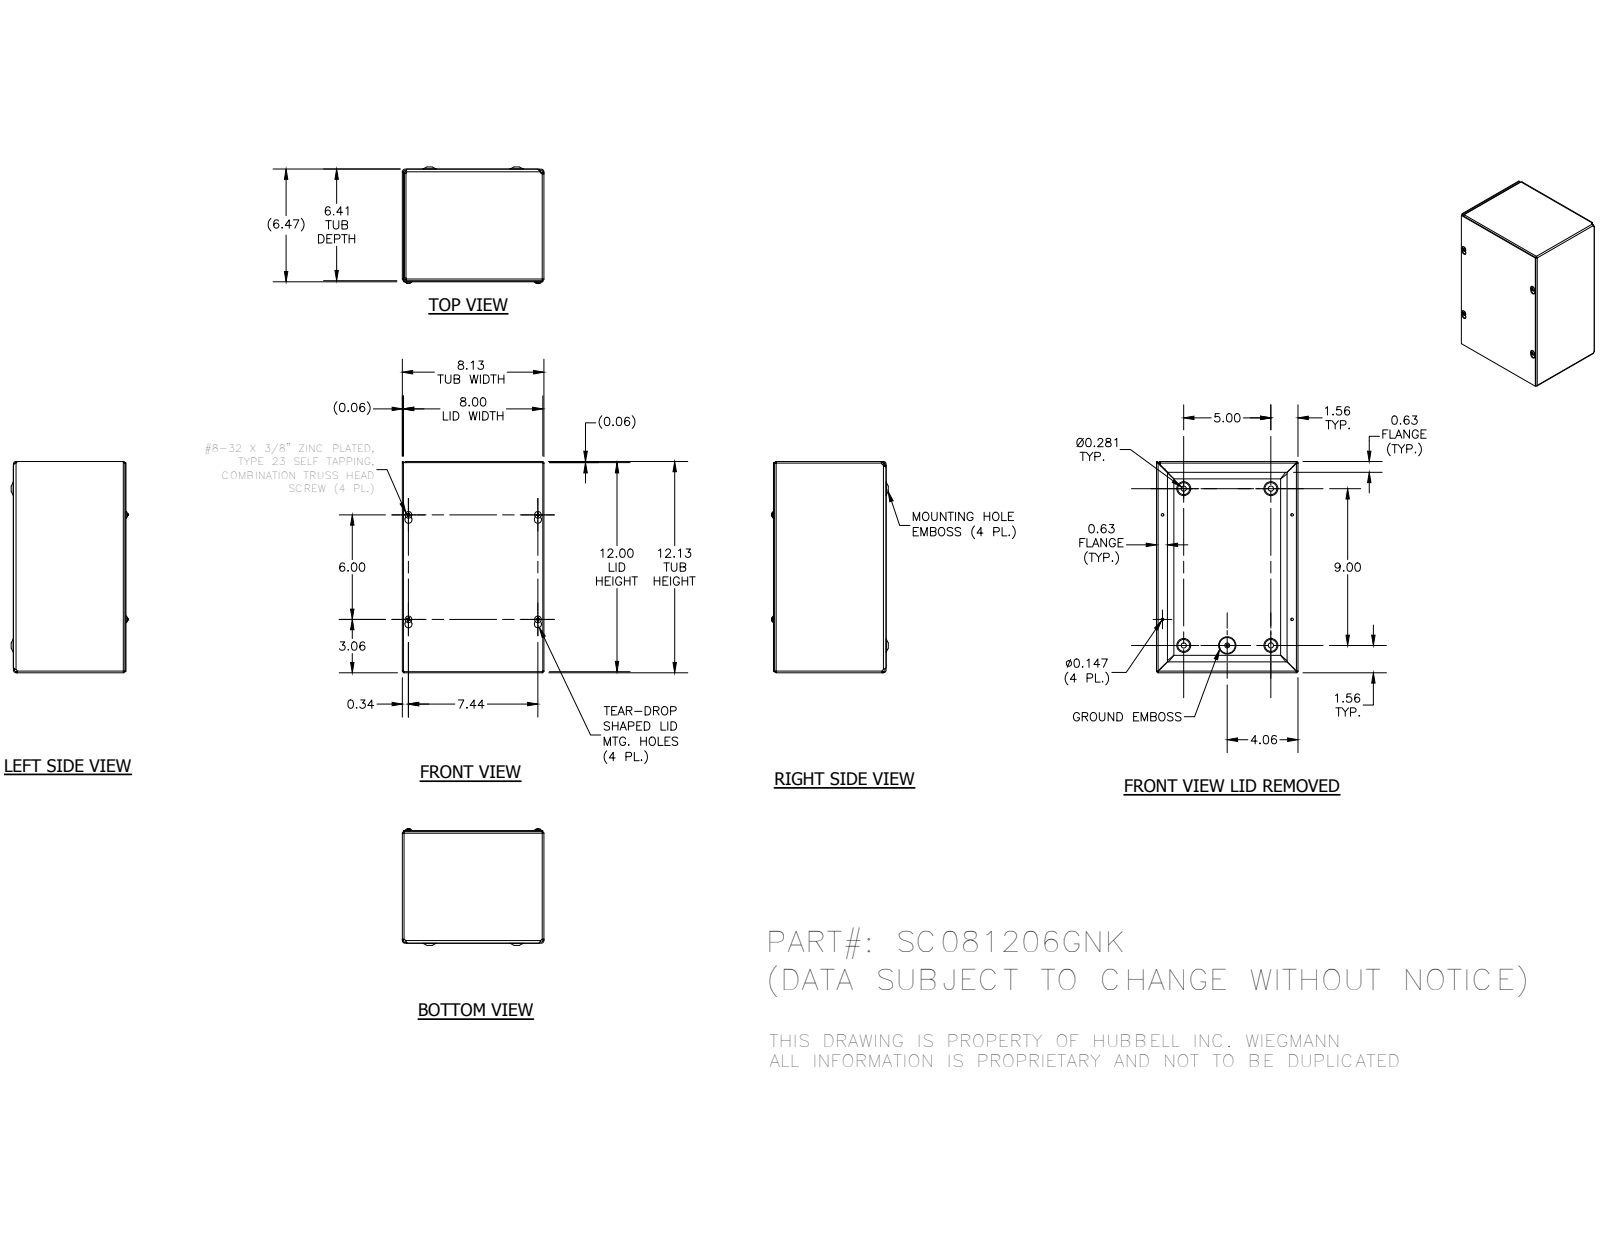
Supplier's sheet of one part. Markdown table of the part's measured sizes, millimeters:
| quantity | value |
| --- | --- |
| part name | SC0812GNKBKP; SC081206GNKWRA; SC0812GNKLID; 34056 (+1 more) |
| STEP written by | Autodesk Inventor 2014 (AUTOMOTIVE_DESIGN) |
| units | millimeters |
| bodies | 7 solids, 358 faces (133 planar, 73 cylindrical, 152 other) |
| overall size | 307.98 × 206.38 × 170 |
| volume | 505 959 mm³ |
| surface area | 649 829 mm² |
| round holes (diameter × count) | 3.73 × 4, 7.62 × 4, 4.19 × 1 |
| round bosses / shafts (diameter × count) | 9.75 × 4, 4.17 × 4, 5.8 × 1 |
| partial cylindrical surfaces (radius × count) | 0.79 × 8, 2.37 × 8, 1.4 × 4, 1.57 × 4, 2.38 × 4, 2.97 × 4, 3.15 × 4, 3.17 × 4 |
| main face-to-face distances | 1.57, 204.8, 161.12, 162.69, 1.59, 162.71, 164.28, 206.37, 203.23, 1.58 |
| hole center spacings | 63.5, 127, 152.4, 162.48, 162.49, 188.91, 192.98, 193.02 |
